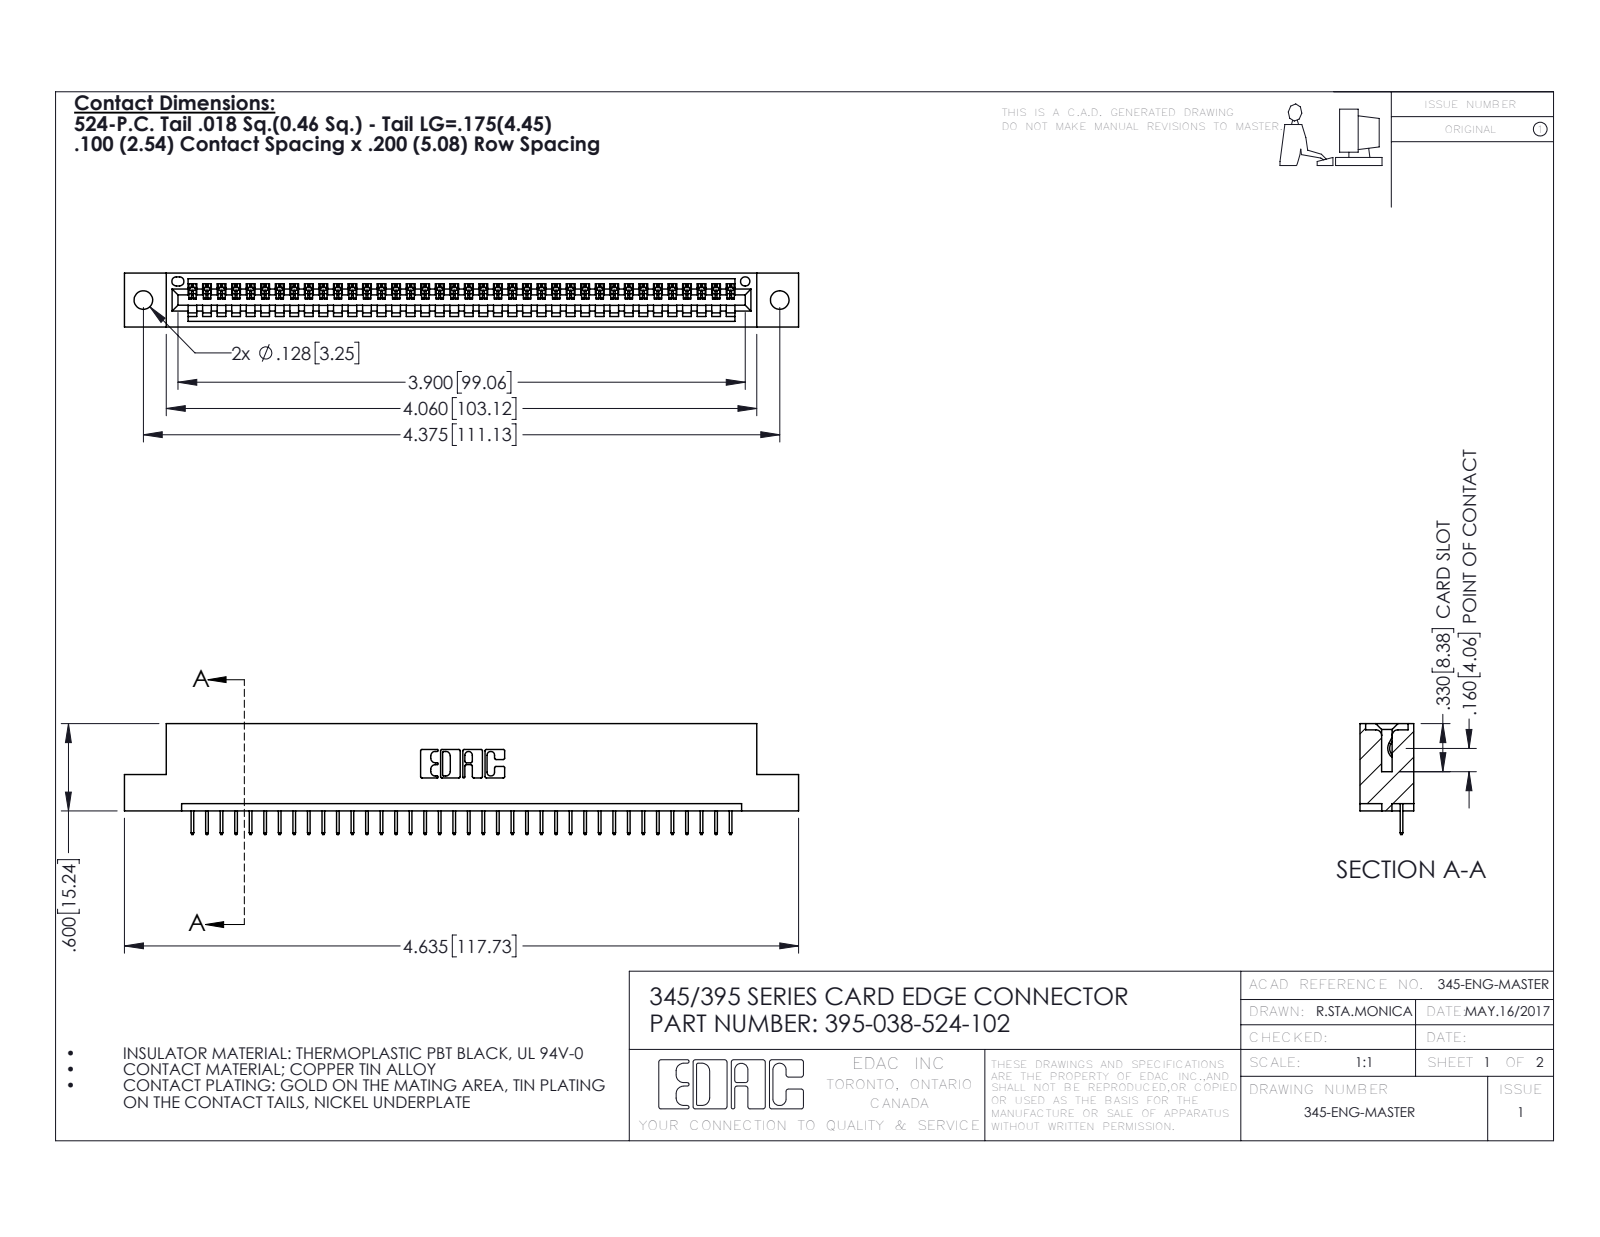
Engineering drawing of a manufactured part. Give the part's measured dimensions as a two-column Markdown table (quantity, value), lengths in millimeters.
| quantity | value |
| --- | --- |
| part name | 345-292-001_345-293-124; 345 Part_Flush Mounting Lugs - 0.128 Dia; 395-038-524-102 |
| STEP written by | SolidWorks 2016 (CONFIG_CONTROL_DESIGN) |
| units | millimeters |
| bodies | 39 solids, 2482 faces (1828 planar, 654 cylindrical, 0 other) |
| overall size | 117.7 × 19.4 × 9.4 |
| volume | 11 000 mm³ |
| surface area | 13 760 mm² |
| round holes (diameter × count) | 3.3 × 2, 1.6 × 1 |
| partial cylindrical surfaces (radius × count) | 0.2 × 76, 0.3 × 22, 0.2 × 6, 0.8 × 6, 0.7 × 3, 0.8 × 2, 1 × 2, 0.4 × 1 |
| main face-to-face distances | 7.6, 1.8, 9.4, 5.1, 2.5, 6.9, 0.6, 5.7, 1.8, 3.8 |
| hole center spacings | 6.9, 105.1, 111.1 |
